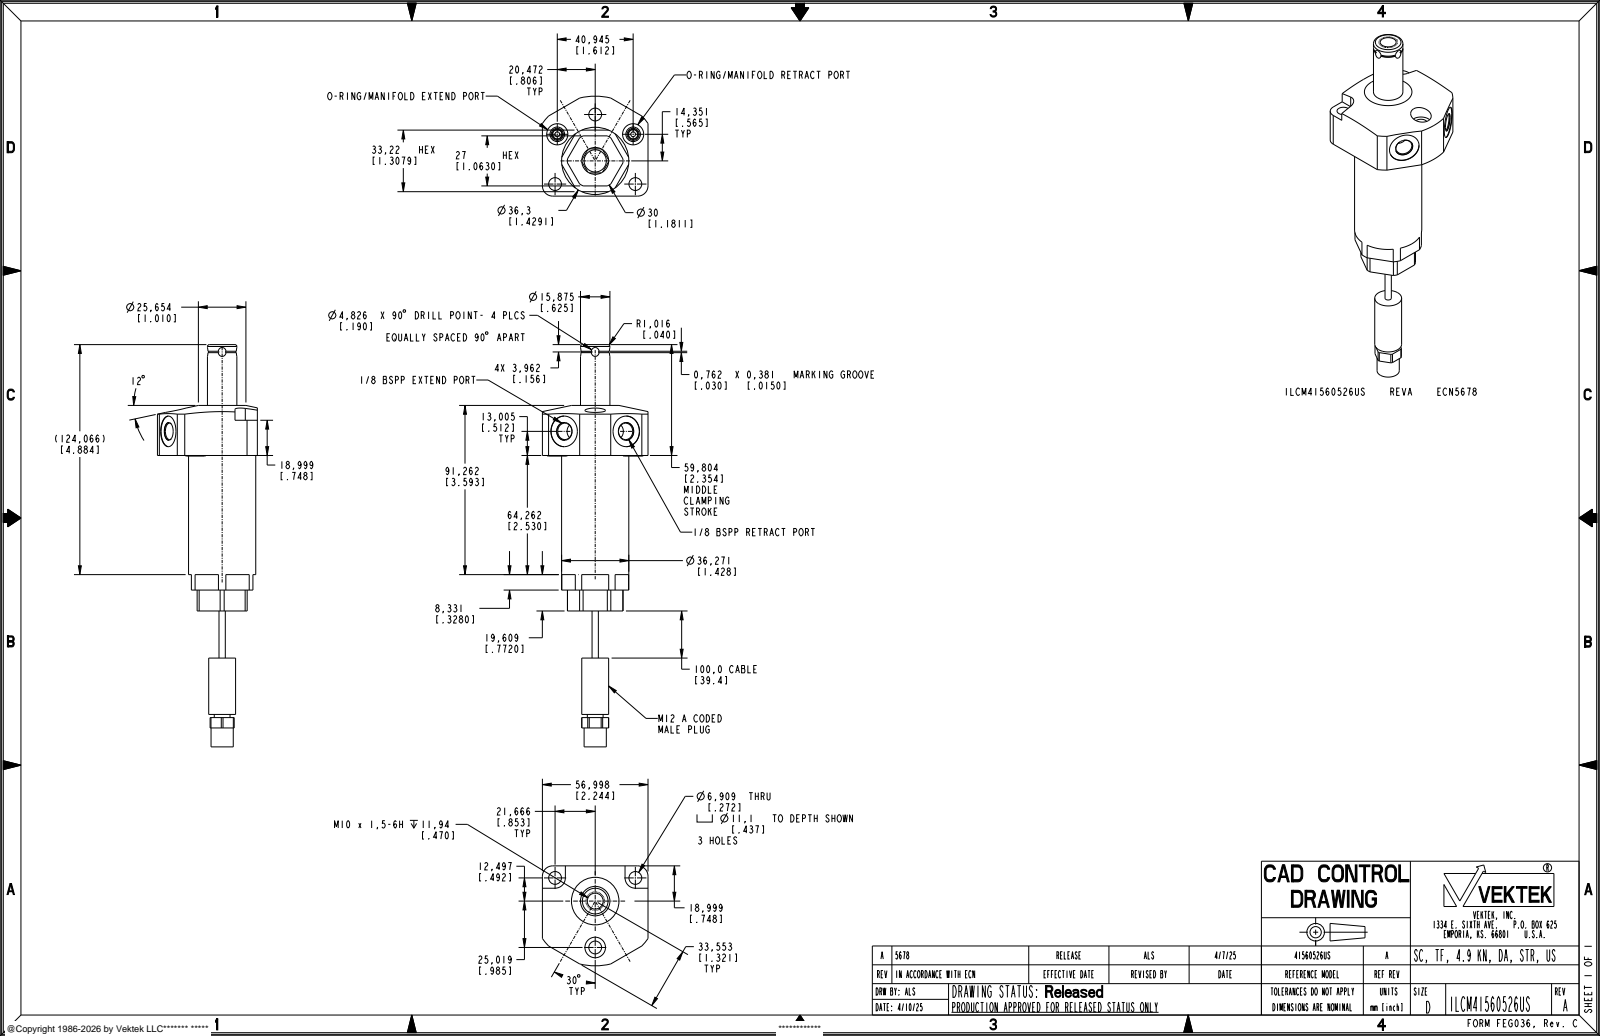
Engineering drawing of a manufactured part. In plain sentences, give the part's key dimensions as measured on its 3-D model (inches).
The part is named "ILCM41560526US". Its 3-D file was written by "CREO PARAMETRIC BY PTC INC, 2021164 (AUTOMOTIVE_DESIGN)". It is 1 solid with 192 faces: 87 planar, 75 cylindrical and 30 other. Overall it measures 8.543 by 2.444 by 2.373 inches. Its volume is 9.616 cubic inches and its surface area 43.94 square inches. Round holes: 3 of diameter 0.272, 2 of diameter 0.098, 2 of diameter 0.256, 2 of diameter 0.348, 2 of diameter 0.449, 2 of diameter 0.65, 1 of diameter 0.339, 1 of diameter 0.437, 1 of diameter 0.895. Round bosses or shafts: 2 of diameter 0.216, 1 of diameter 1.428, 1 of diameter 0.625, 1 of diameter 0.571, 1 of diameter 0.472, 1 of diameter 0.394, 1 of diameter 0.335, 1 of diameter 0.134. Partial cylindrical surfaces (rounded edges, fillets, slot ends): 2 of radius 0.219, 2 of radius 0.219, 1 of radius 0.298, 1 of radius 0.591, 1 of radius 1.375. The main face-to-face distances are 1.063, 2.244, 0.122, 1.185, 3.302, 0.772, 2.53, 0.832, 0.06, 2.47. The hole center spacings are 0.985, 0.909, 0.984, 1.058, 1.706, 1.967, 1.612, 1.706.
